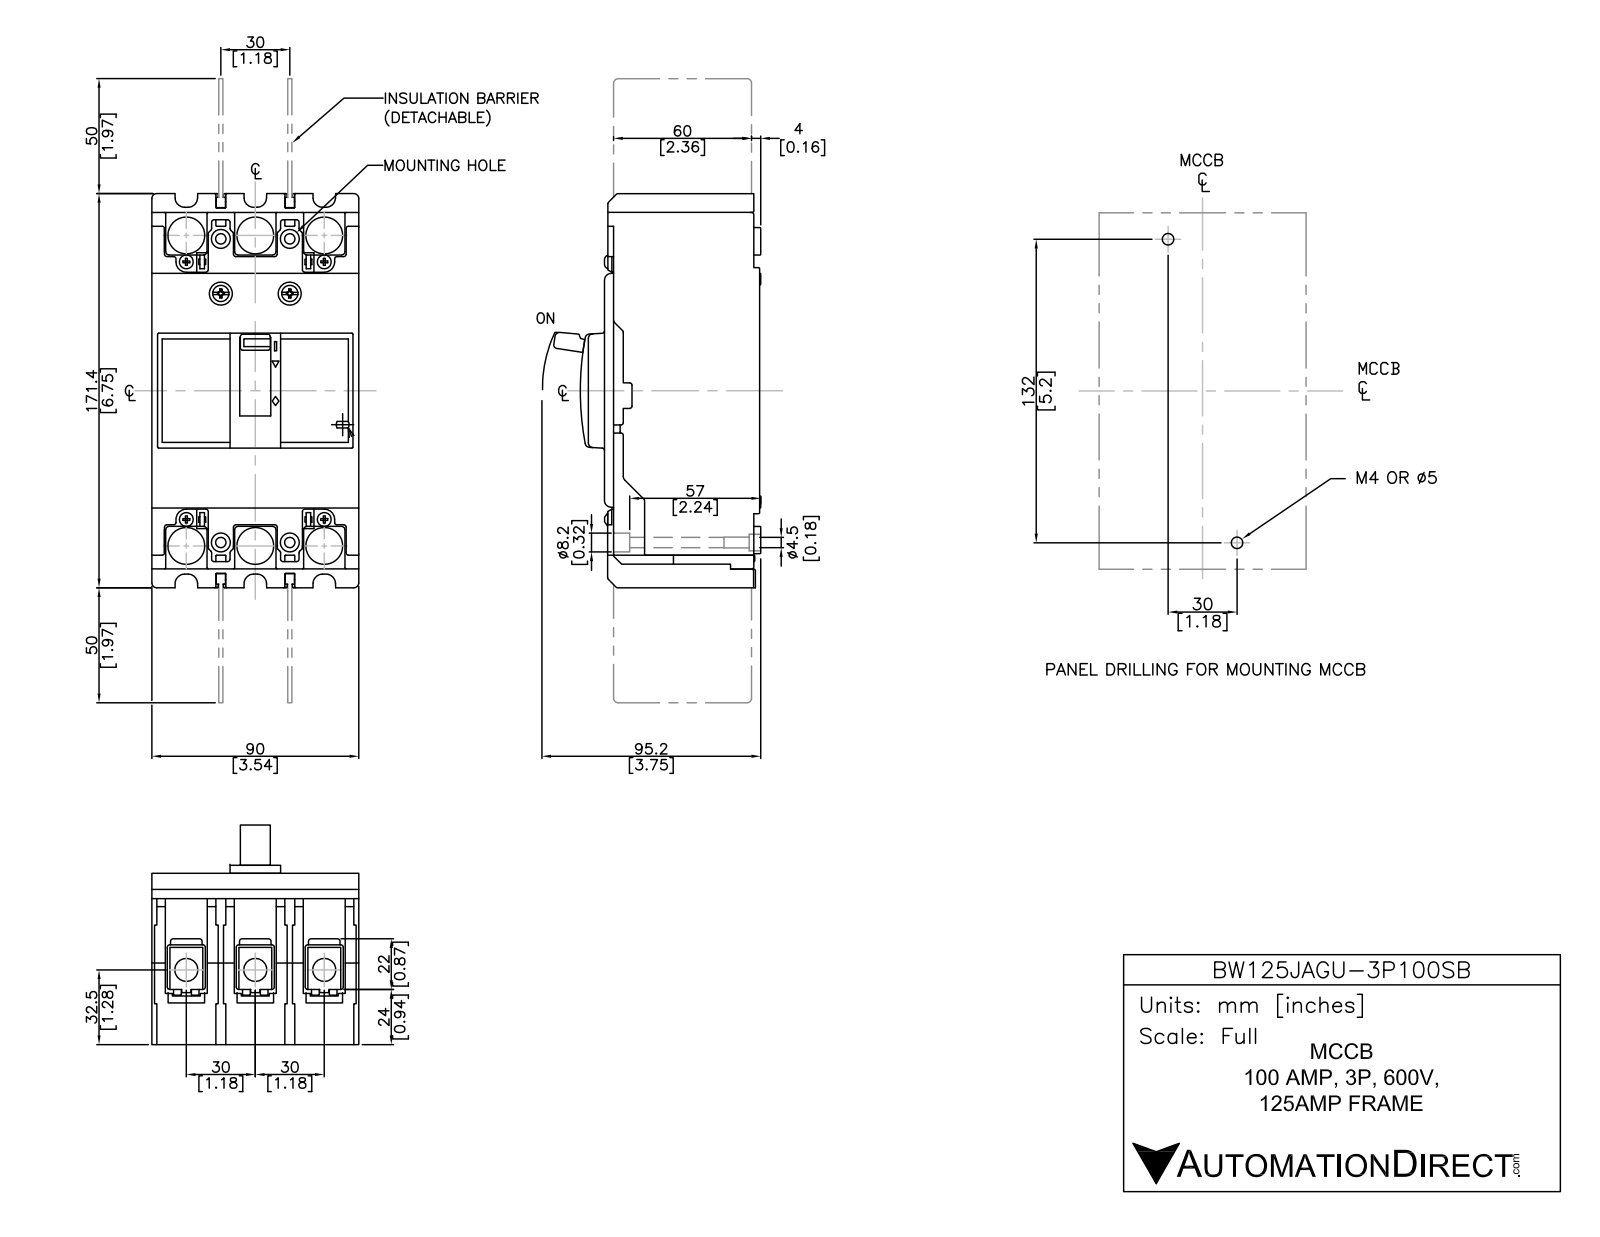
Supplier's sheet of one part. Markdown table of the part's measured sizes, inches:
| quantity | value |
| --- | --- |
| part name | BW125JAGU-3P100SB |
| STEP written by | SolidWorks 2018 (AUTOMOTIVE_DESIGN) |
| units | inches |
| bodies | 14 solids, 452 faces (340 planar, 88 cylindrical, 24 other) |
| overall size | 10.197 × 3.602 × 3.543 |
| volume | 57.4 in³ |
| surface area | 230.3 in² |
| round holes (diameter × count) | 0.315 × 6, 0.177 × 4, 0.323 × 4 |
| round bosses / shafts (diameter × count) | 0.472 × 6 |
| partial cylindrical surfaces (radius × count) | 0.157 × 12, 0.079 × 6, 0.118 × 6 |
| main face-to-face distances | 1.181, 1.11, 1.252, 2.291, 2.433, 0.142, 3.543, 0.236, 2.402, 1.039 |
| hole center spacings | 0.593, 5.289, 1.181, 1.772, 5.444, 5.546, 5.315, 2.362 |
